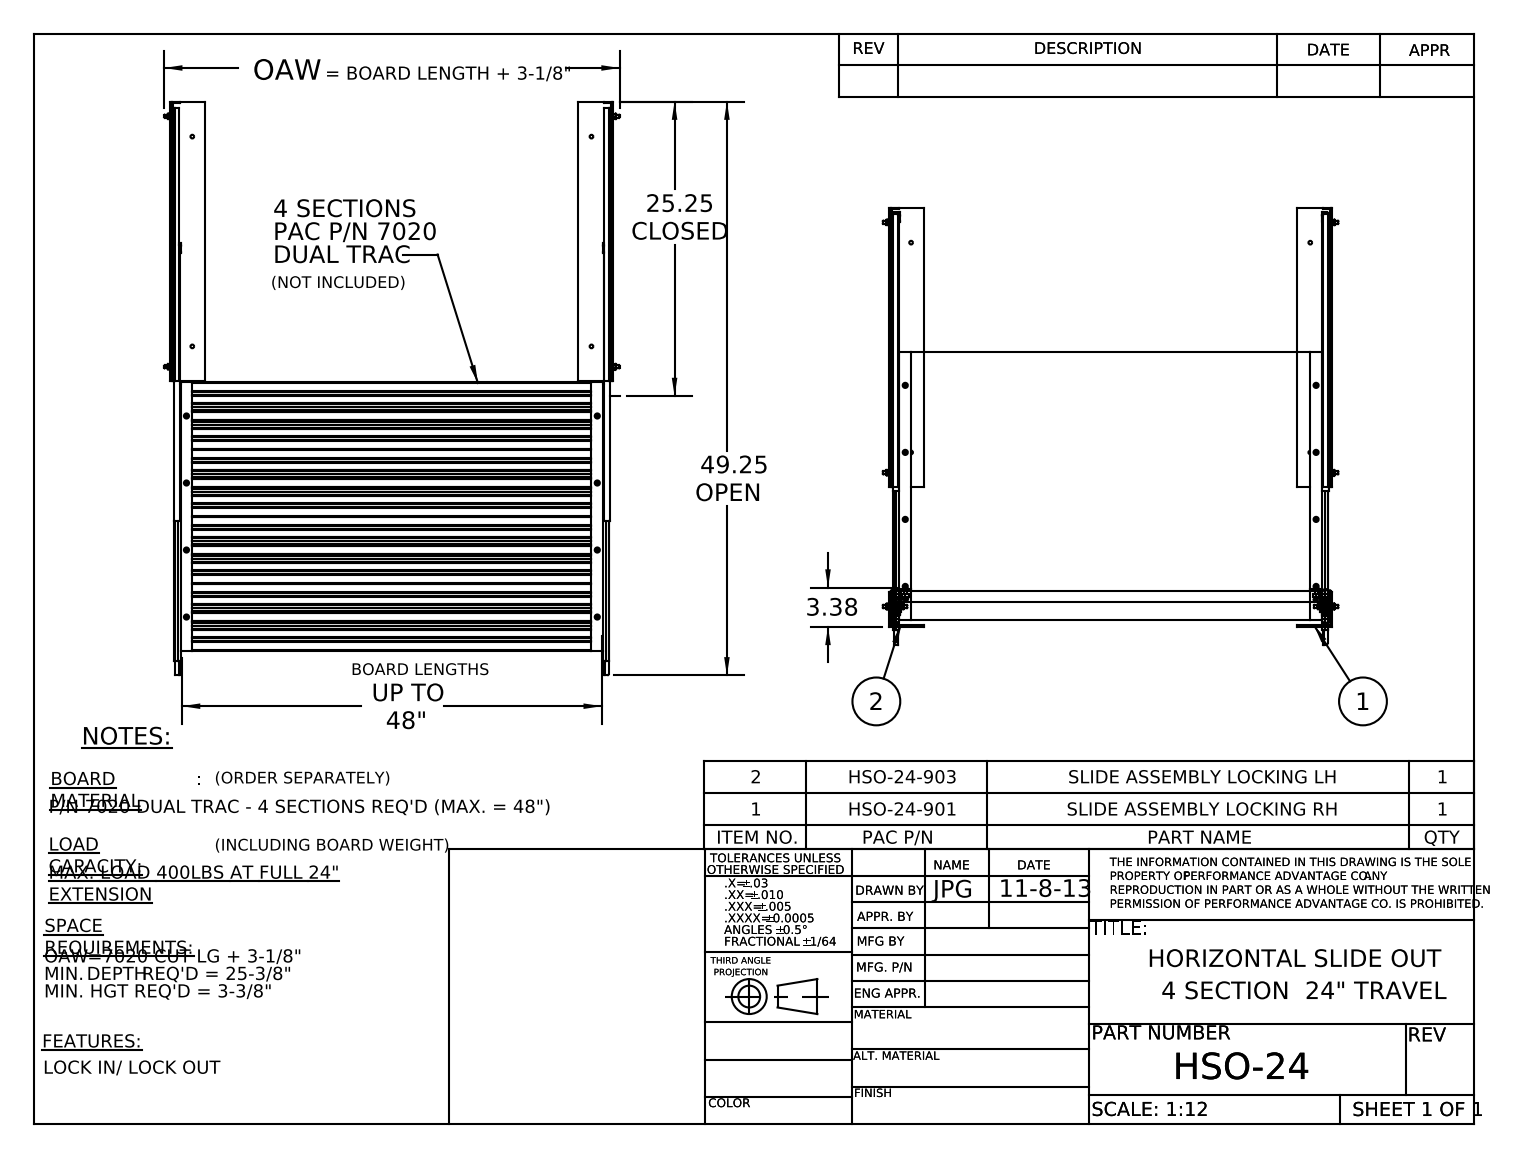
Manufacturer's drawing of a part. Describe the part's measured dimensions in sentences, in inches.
The part is named "HSO-24-901; HSO-24-903; FA 776-4397 LH; SO-24-201 (+8 more)". Its 3-D file was written by "SolidWorks 2014 (CONFIG_CONTROL_DESIGN)". It is 48 solids with 1823 faces: 1004 planar, 611 cylindrical and 208 other. Overall it measures 49.22 by 39.061 by 3.382 inches. Its volume is 307.7 cubic inches and its surface area 6 027 square inches. Round holes: 14 of diameter 0.201, 11 of diameter 0.266, 8 of diameter 0.313, 8 of diameter 0.332, 7 of diameter 0.26, 6 of diameter 0.25, 6 of diameter 0.269, 2 of diameter 0.328, 2 of diameter 1.039. Round bosses or shafts: 14 of diameter 0.437, 8 of diameter 0.25, 6 of diameter 0.404. Partial cylindrical surfaces (rounded edges, fillets, slot ends): 48 of radius 0.092, 32 of radius 0.03, 24 of radius 0.031, 17 of radius 0.063, 16 of radius 0.031, 16 of radius 0.469, 10 of radius 0.02, 10 of radius 0.039. The main face-to-face distances are 0.875, 0.082, 5.75, 5.589, 0.082, 0.793, 0.125, 11.5, 0.125, 11.178. The hole center spacings are 5.75, 11.5, 35.716, 0.75, 35.25, 37.078, 17.25, 18.
